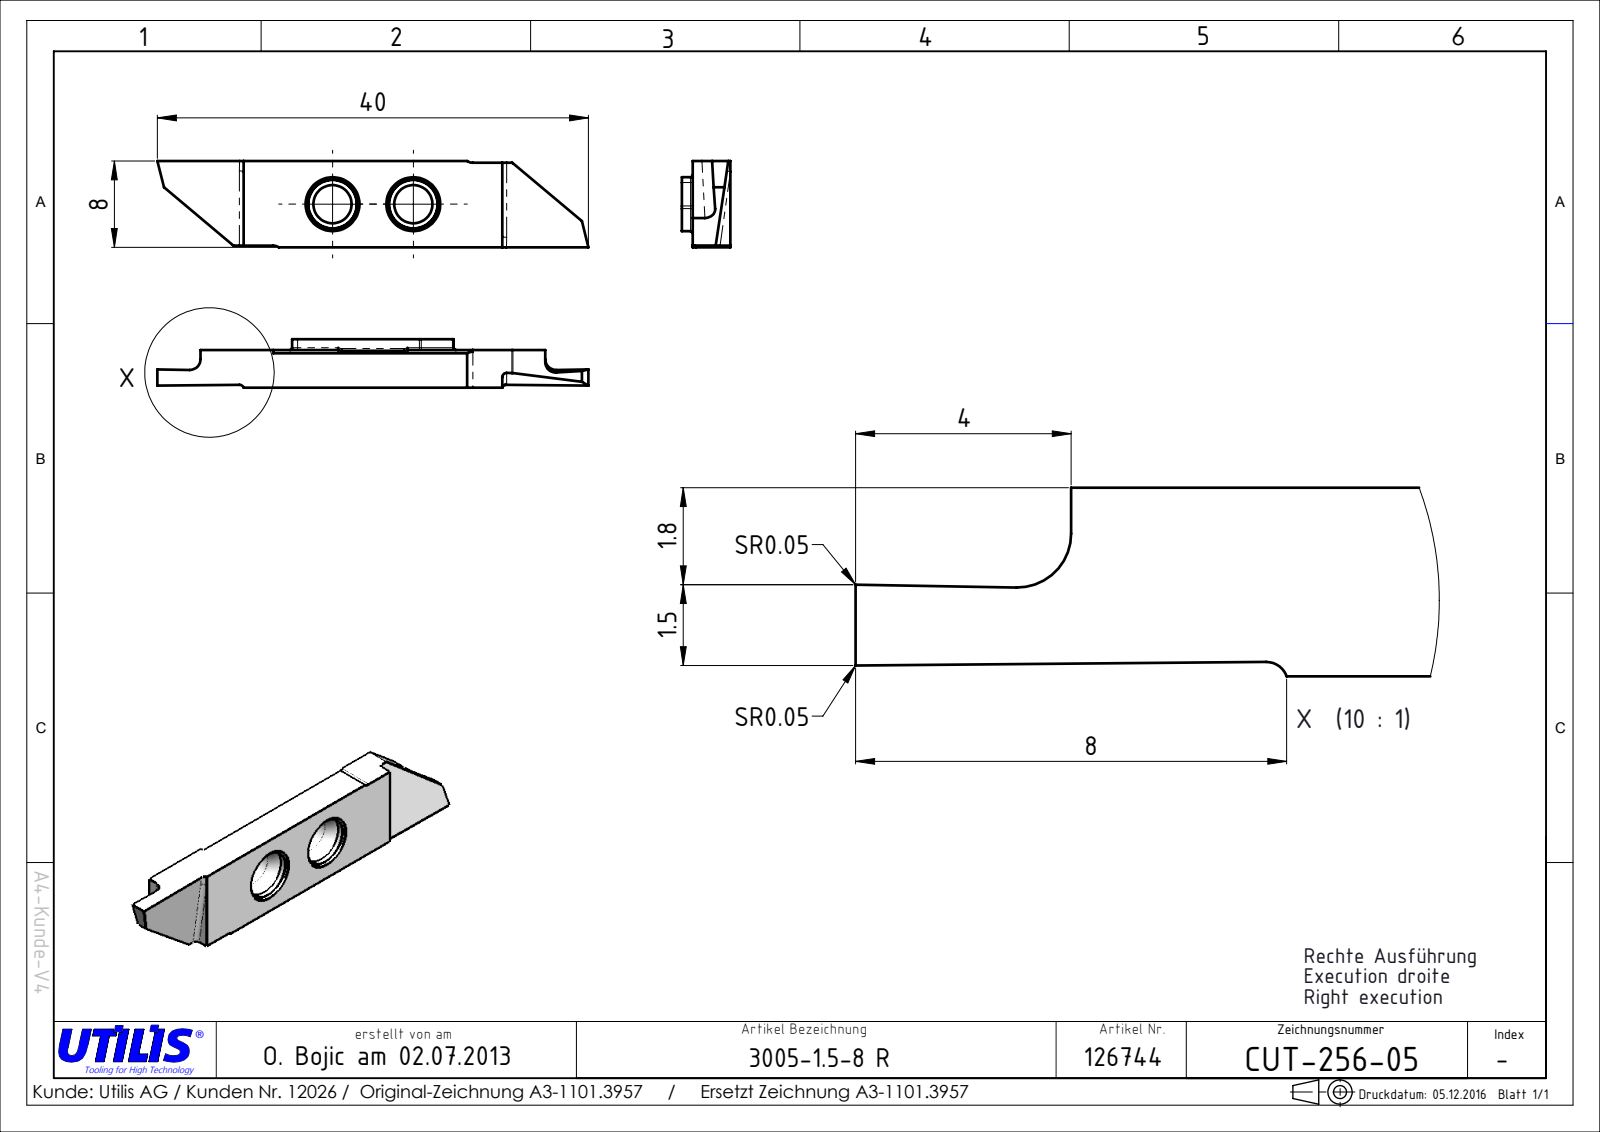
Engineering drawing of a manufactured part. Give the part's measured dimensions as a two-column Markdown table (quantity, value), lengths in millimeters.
| quantity | value |
| --- | --- |
| part name | CUT-256-05 |
| STEP written by | SolidWorks 2016 (AUTOMOTIVE_DESIGN) |
| units | millimeters |
| bodies | 1 solid, 38 faces (24 planar, 14 cylindrical, 0 other) |
| overall size | 40 × 8 × 3.5 |
| volume | 820 mm³ |
| surface area | 858 mm² |
| round holes (diameter × count) | 3.55 × 2 |
| partial cylindrical surfaces (radius × count) | 0.15 × 4, 1 × 4, 0.4 × 2 |
| main face-to-face distances | 3.5, 8, 7.85, 22.54, 7.7, 4, 36, 32, 40, 38.98 |
| hole center spacings | 7.5 |
